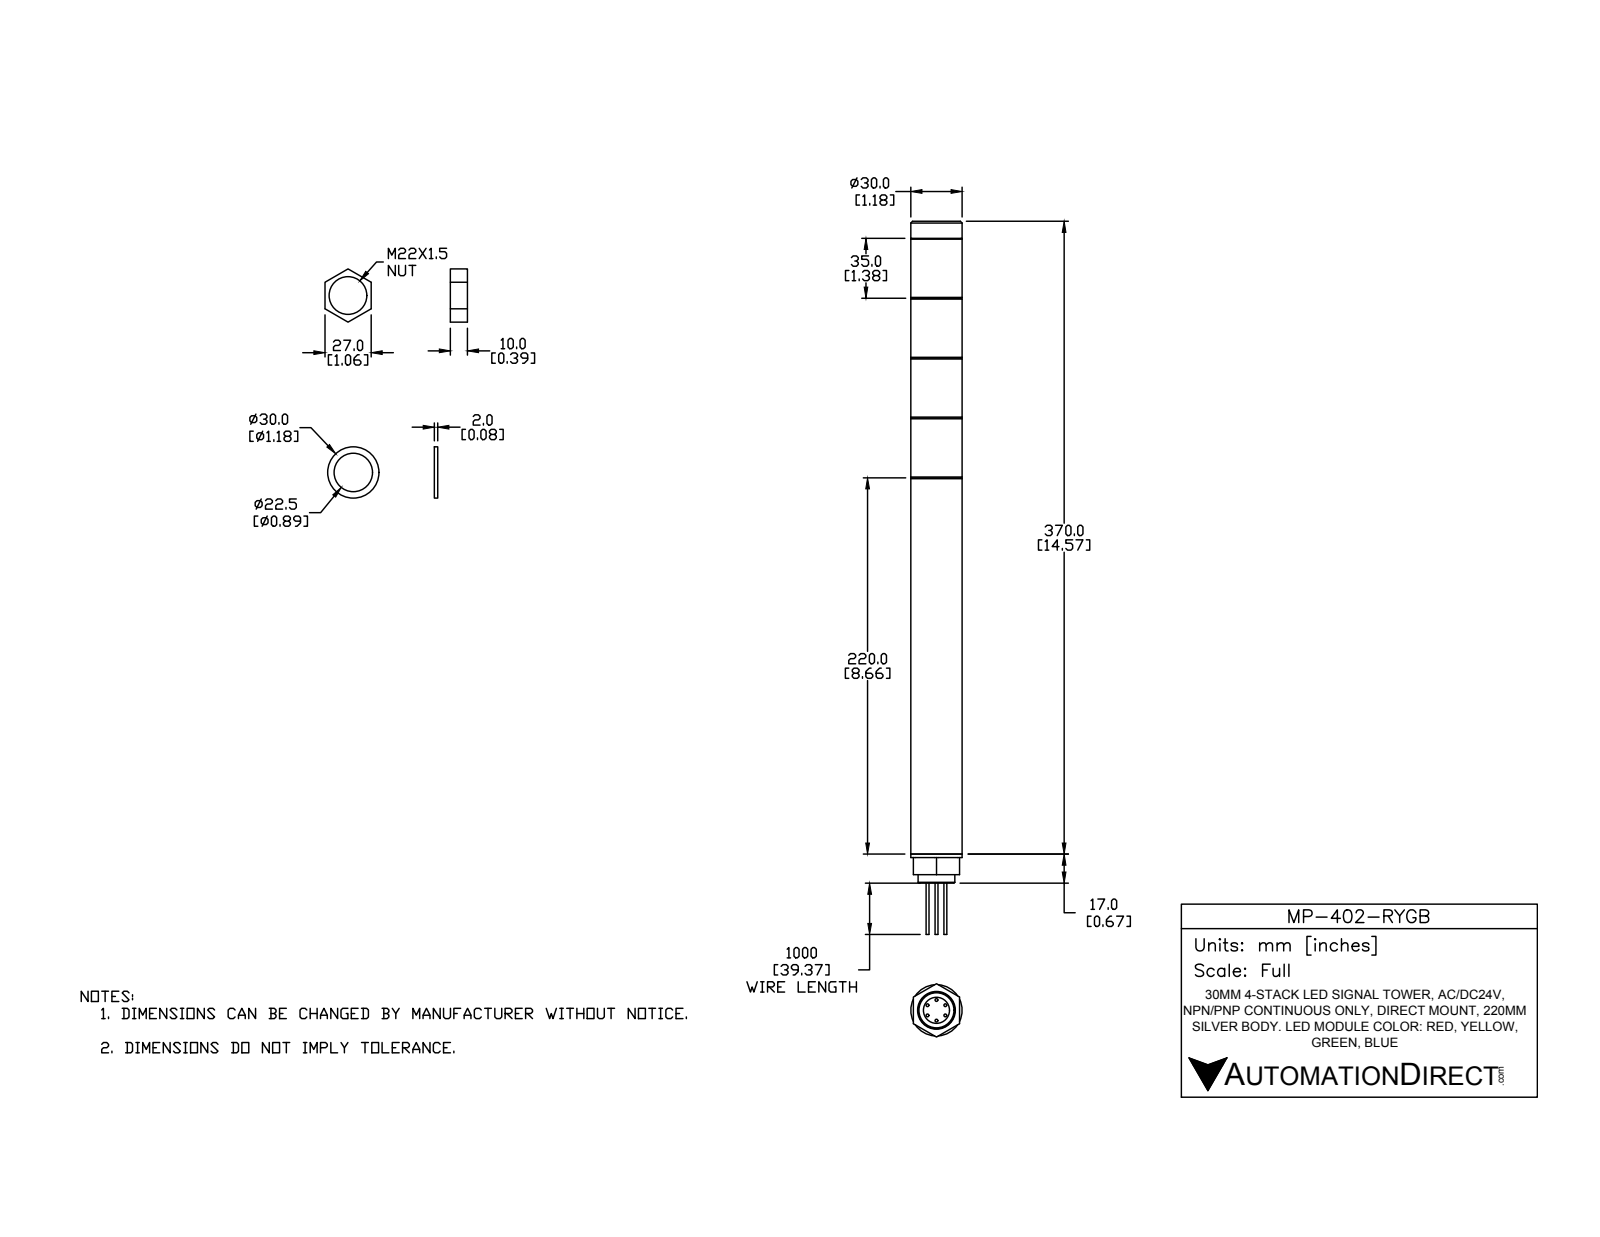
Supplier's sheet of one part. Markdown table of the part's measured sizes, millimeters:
| quantity | value |
| --- | --- |
| part name | MP-402-RYGB |
| STEP written by | SolidWorks 2016 (AUTOMOTIVE_DESIGN) |
| units | millimeters |
| bodies | 15 solids, 119 faces (53 planar, 42 cylindrical, 24 other) |
| overall size | 417 × 31.18 × 30 |
| volume | 257 464 mm³ |
| surface area | 53 403 mm² |
| round holes (diameter × count) | 3.2 × 1, 7.7 × 1, 15.3 × 1, 20.7 × 1, 22 × 1 |
| round bosses / shafts (diameter × count) | 1.7 × 6, 30 × 1, 21.5 × 1, 5 × 1 |
| main face-to-face distances | 35, 70, 105, 140, 222, 257, 292, 327, 45, 372 |
